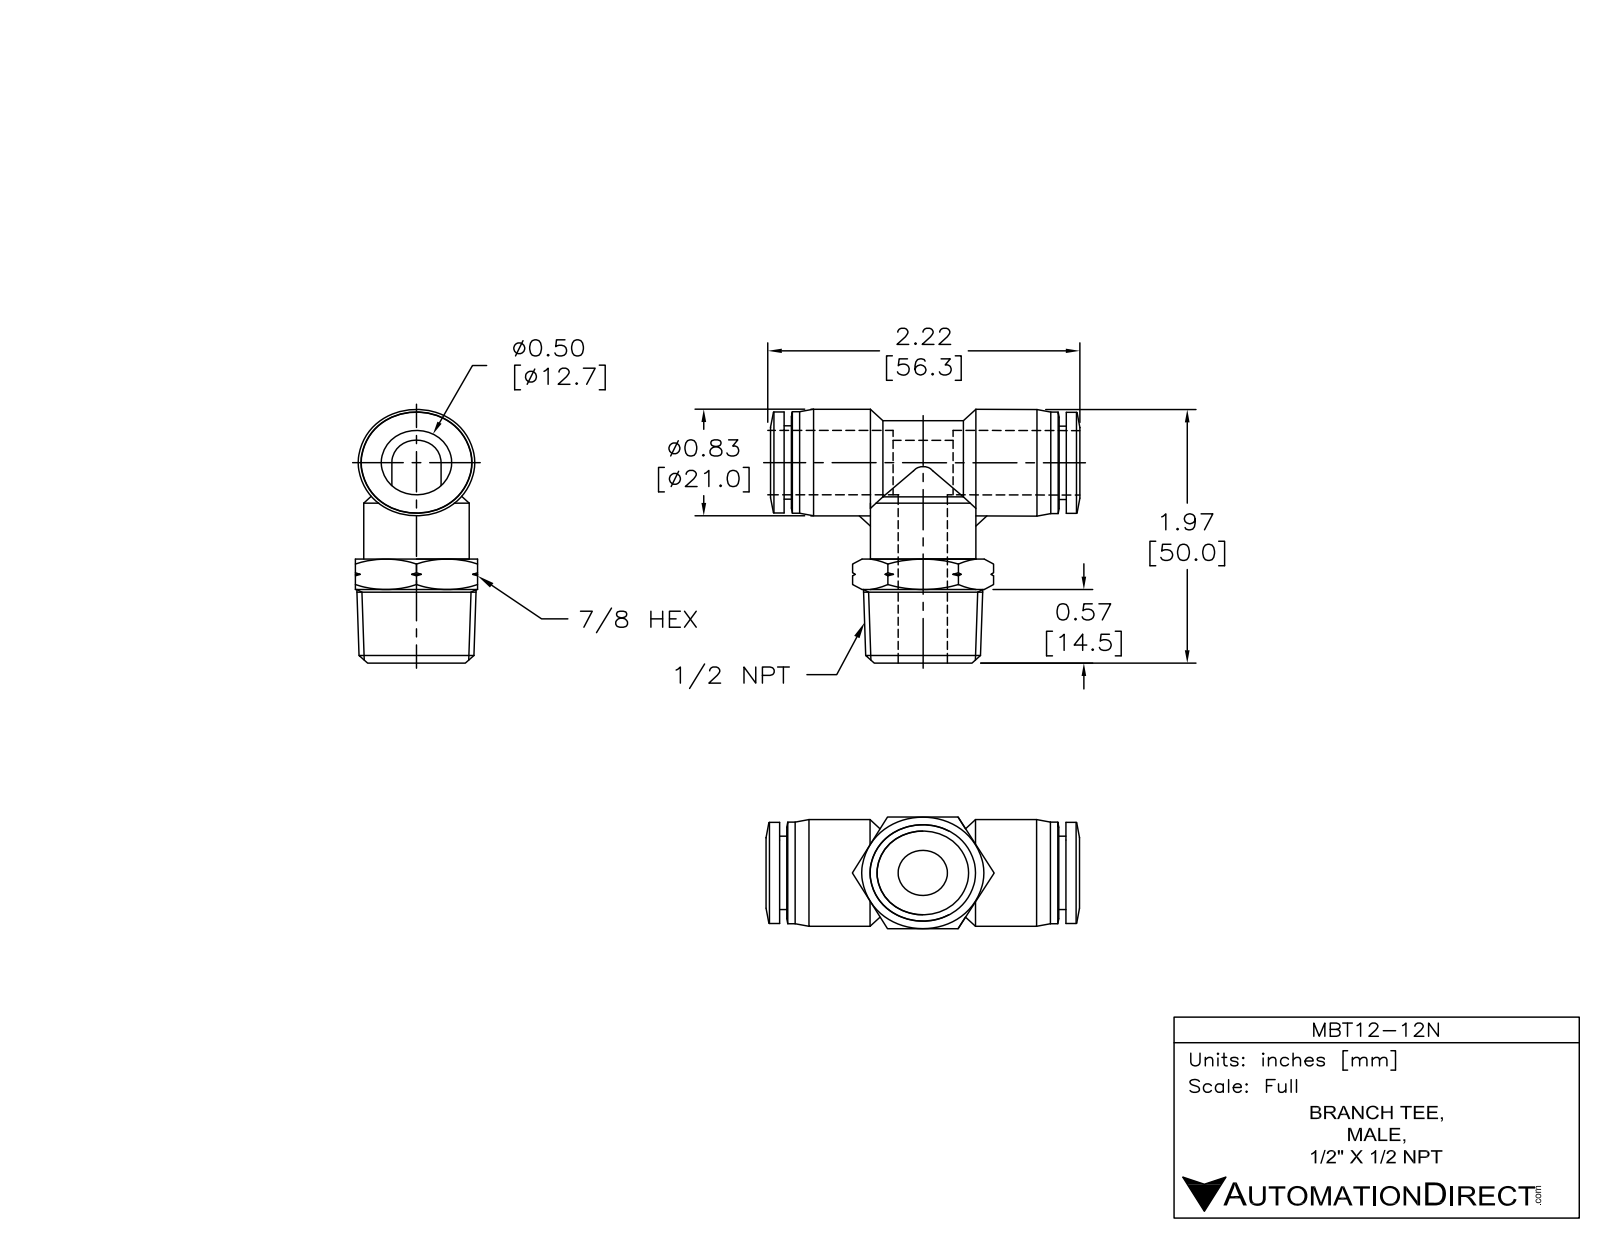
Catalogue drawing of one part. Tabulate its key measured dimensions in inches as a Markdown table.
| quantity | value |
| --- | --- |
| part name | MBT12-12N |
| STEP written by | SolidWorks 2015 (AUTOMOTIVE_DESIGN) |
| units | inches |
| bodies | 1 solid, 114 faces (21 planar, 31 cylindrical, 62 other) |
| overall size | 2.224 × 1.969 × 0.866 |
| volume | 1.111 in³ |
| surface area | 15.33 in² |
| round holes (diameter × count) | 0.354 × 2, 0.51 × 1 |
| round bosses / shafts (diameter × count) | 0.827 × 1, 0.787 × 1, 0.783 × 1, 0.748 × 1, 0.65 × 1, 0.569 × 1 |
| partial cylindrical surfaces (radius × count) | 0.325 × 1 |
| main face-to-face distances | 0.866, 0.051, 1.98, 2.031, 0.813, 1.219, 0.762, 1.167, 0.807, 1.929 |
